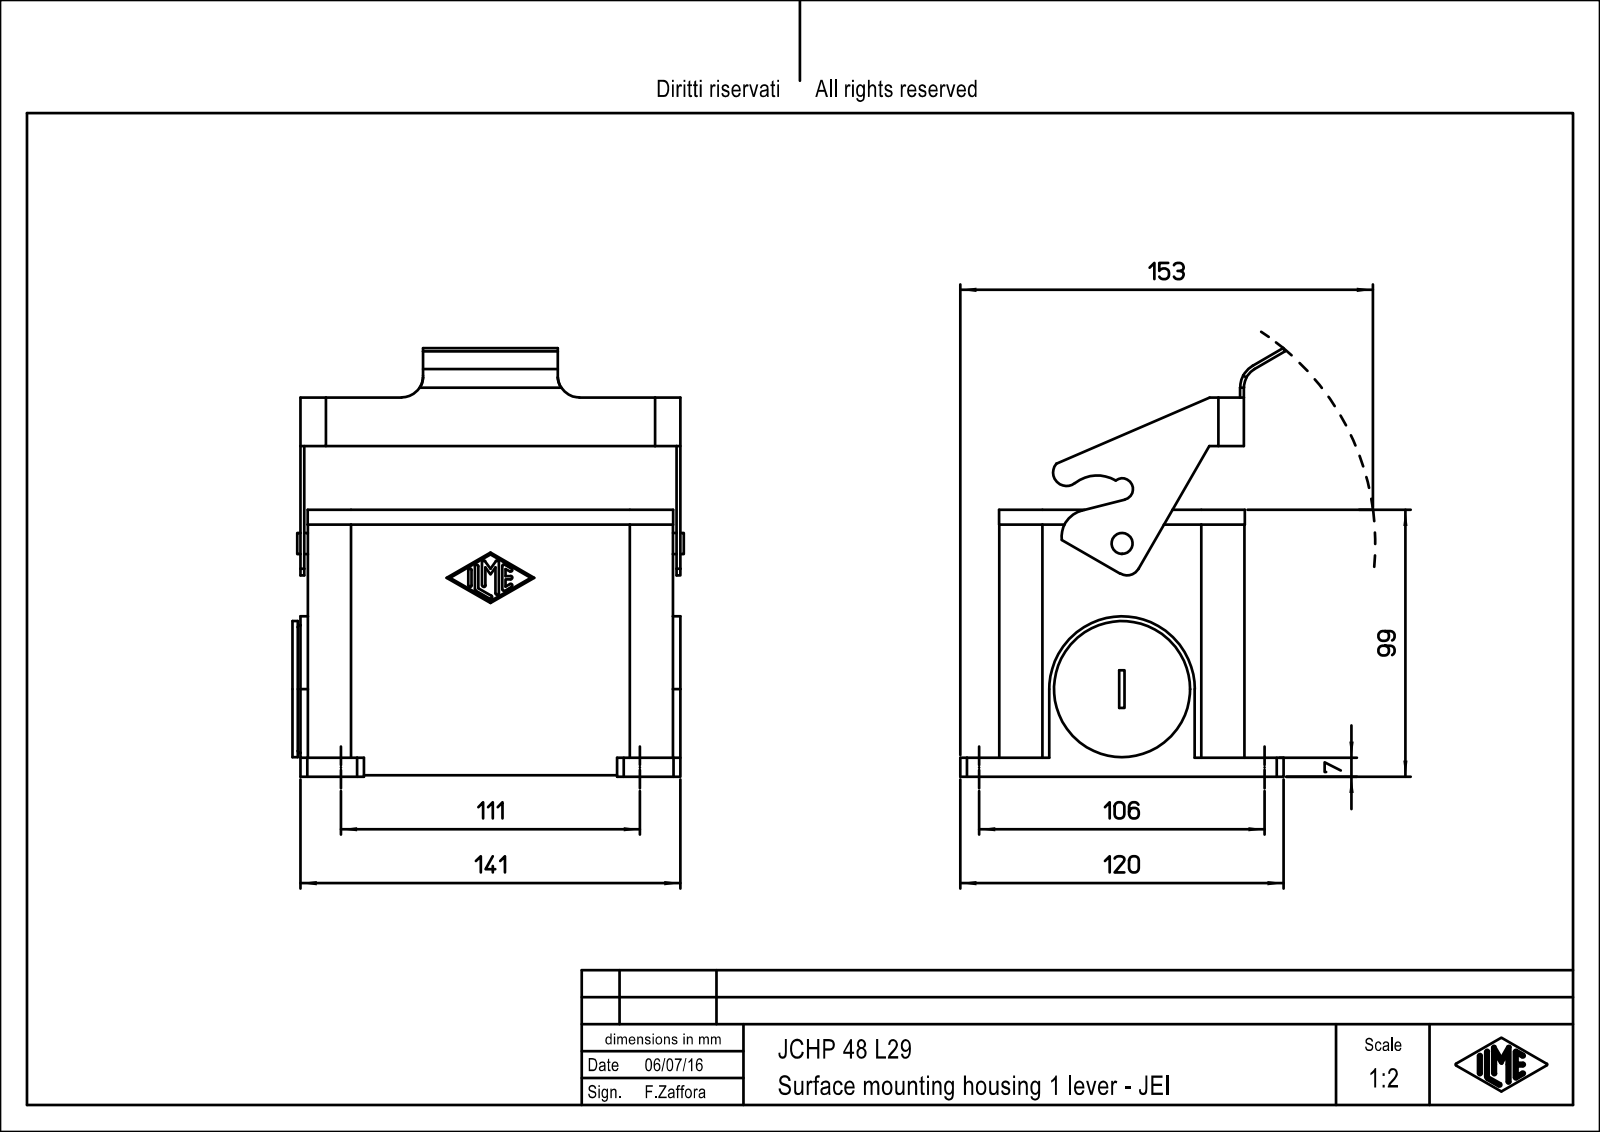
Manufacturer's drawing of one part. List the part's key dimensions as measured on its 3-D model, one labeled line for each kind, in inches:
Part name (STEP PRODUCT): JCHP_48_L29
STEP written by: PTC Creo Elements/Direct Modeling 19.0B 21-Mar-2015 (C) Parametric Technology GmbH (AUTOMOTIVE_DESIGN)
Units: inches
Bodies: 1 solid, 288 faces (166 planar, 118 cylindrical, 4 other)
Overall size (bounding box): 6.012 × 5.719 × 4.823
Volume: 23.42 in³ · Surface area: 208.7 in²
Round holes (diameter × count): ⌀0.122 ×8, ⌀0.256 ×4, ⌀1.398 ×1, ⌀1.457 ×1
Round bosses / shafts (diameter × count): ⌀1.987 ×1, ⌀0.307 ×1
Partial cylindrical surfaces — rounded edges, fillets, slot ends (radius × count): R0.015 ×14, R0.039 ×9, R0.098 ×8, R0.315 ×5, R0.429 ×4, R0.433 ×4, R0.63 ×4, R0.634 ×4
Main face-to-face distances: 0.197, 3.386, 3.583, 3.189, 0.856, 0.157, 4.695, 0.02, 0.055, 0.177
Hole centre spacings: 4.32, 0.877, 1.063, 1.378, 1.934, 2.248, 3.31, 4.094
